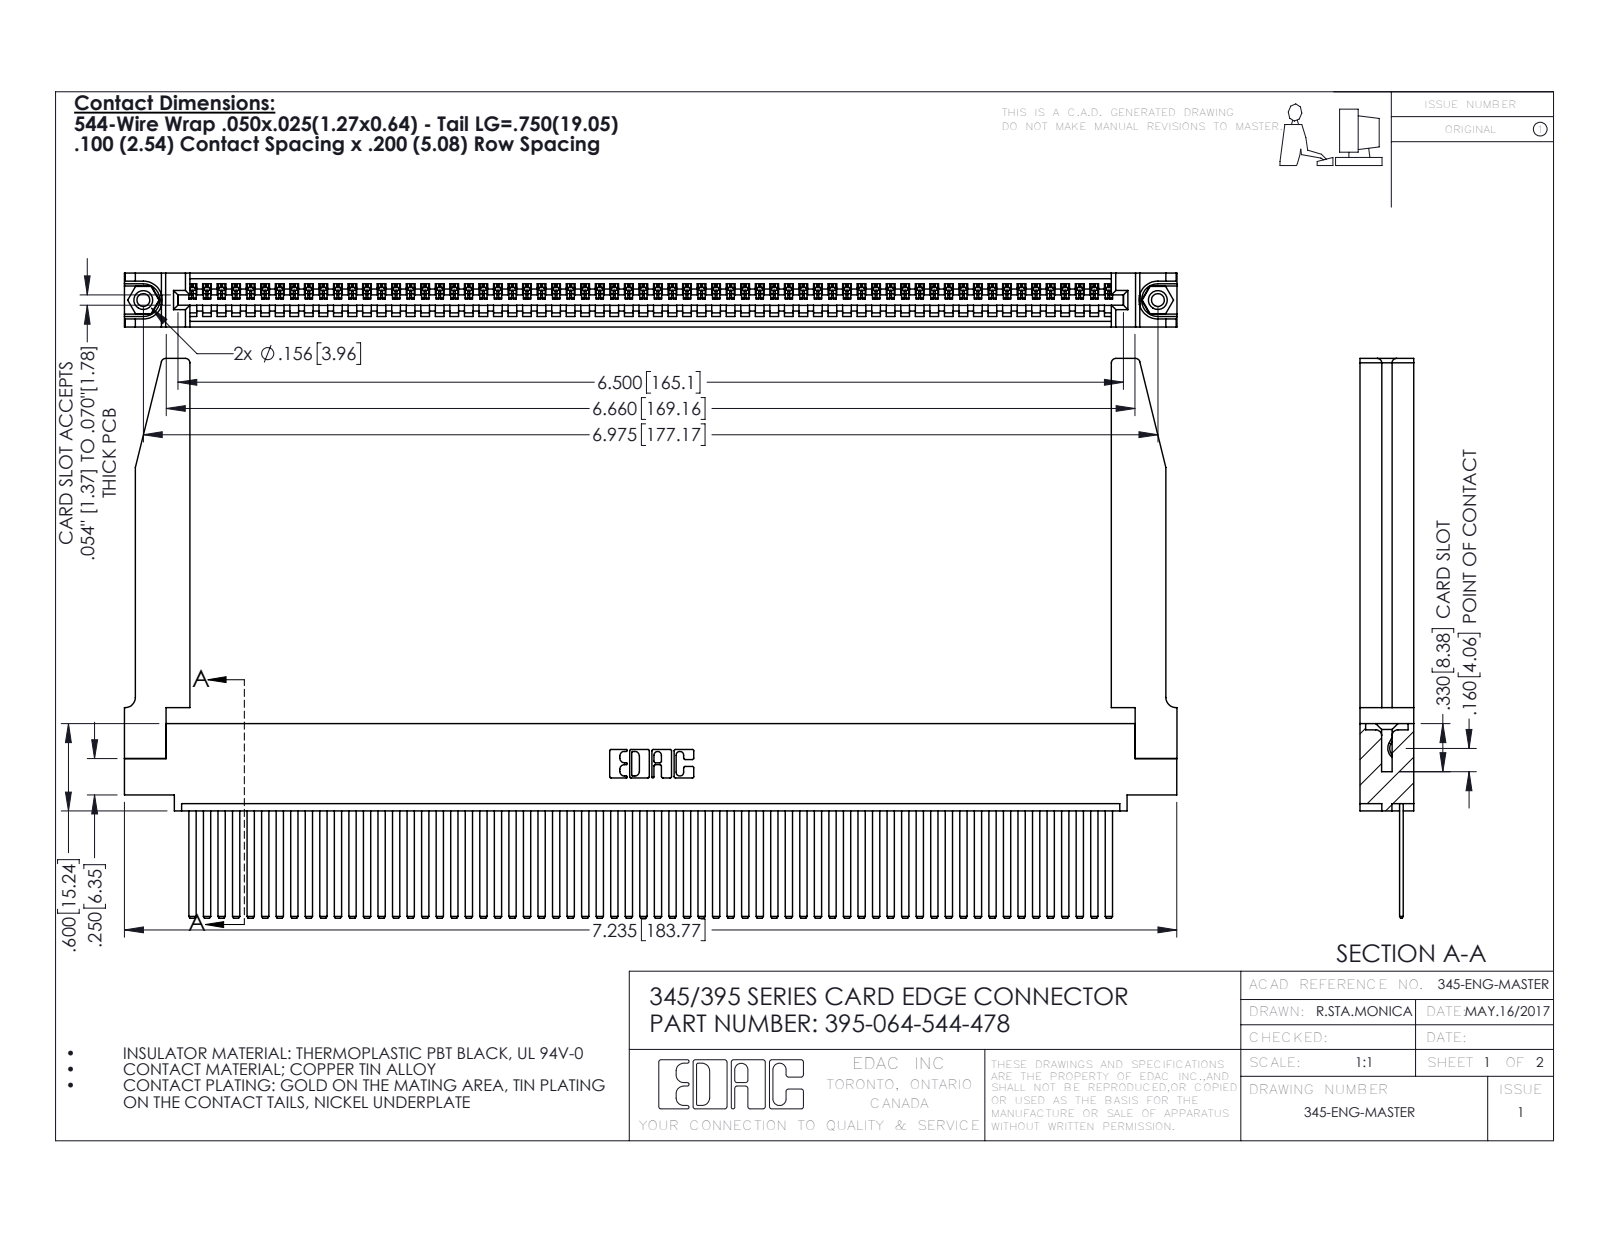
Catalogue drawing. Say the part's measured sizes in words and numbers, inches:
The part is named "395-064-544-478; 345 Part_0.110 Offset - 0.156 Dia-TH; 345-292-001_345-293-144; 345-220-078_345-220-078 (+1 more)". Its 3-D file was written by "SolidWorks 2016 (CONFIG_CONTROL_DESIGN)". It is 69 solids with 3692 faces: 2530 planar, 1110 cylindrical and 52 other. Overall it measures 7.236 by 3.847 by 0.37 inches. Its volume is 1.591 cubic inches and its surface area 52.36 square inches. Round holes: 2 of diameter 0.089, 2 of diameter 0.125, 2 of diameter 0.156, 1 of diameter 0.064. Round bosses or shafts: 2 of diameter 0.155. Partial cylindrical surfaces (rounded edges, fillets, slot ends): 128 of radius 0.006, 22 of radius 0.01, 8 of radius 0.03, 6 of radius 0.007, 6 of radius 0.031, 3 of radius 0.026, 2 of radius 0.031, 2 of radius 0.04. The main face-to-face distances are 0.072, 0.298, 0.37, 0.098, 0.272, 0.025, 0.2, 0.225, 0.148, 0.15. The hole center spacings are 0.27, 6.739, 6.975.
